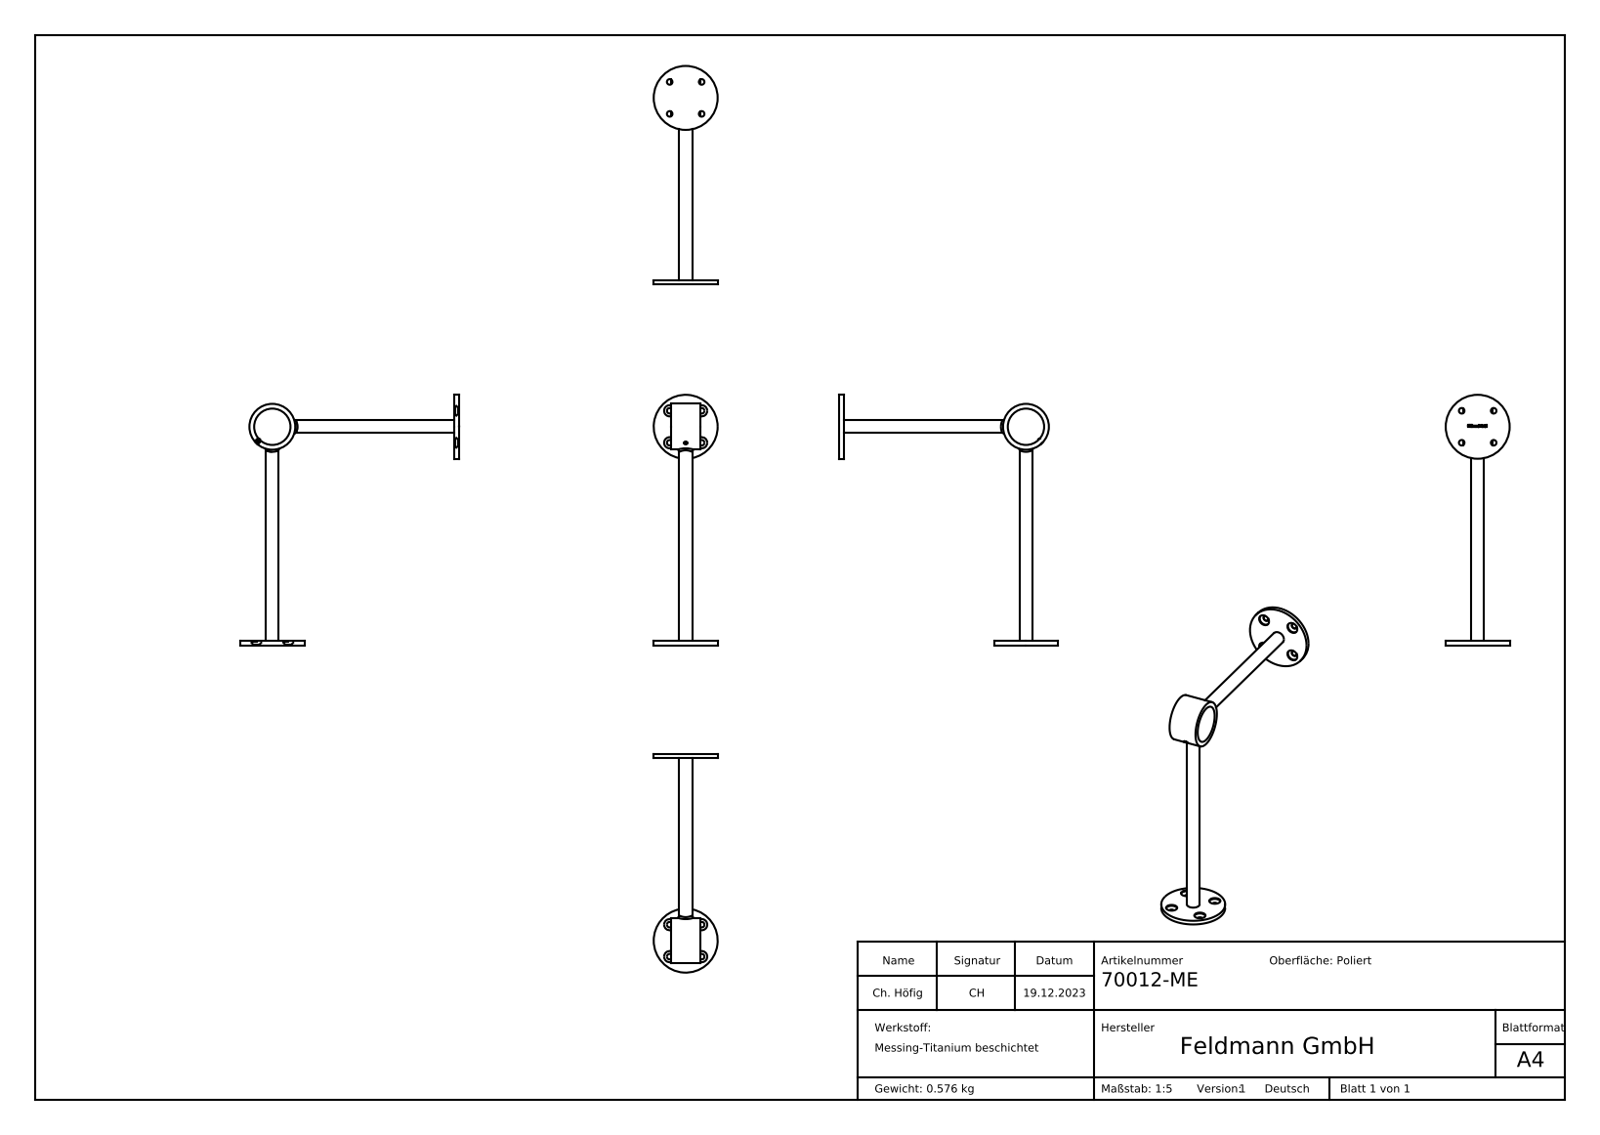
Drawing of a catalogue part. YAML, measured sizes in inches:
part_name: "70012-ME; DIN913_DIN 913 M4x5; 70012-ME Teil1_70012-ME Teil1"
step_written_by: "SolidWorks 2018 (CONFIG_CONTROL_DESIGN)"
units: inches
bodies: {solids: 2, faces: 251, planar: 142, cylindrical: 24, other: 85}
overall_size: [9.252, 8.071, 2.362]
volume: 4.451
surface_area: 50.86
round_holes:
  - {diameter: 0.205, count: 8}
  - {diameter: 0.413, count: 8}
  - {diameter: 0.13, count: 1}
  - {diameter: 1.343, count: 1}
round_bosses_or_shafts:
  - {diameter: 2.362, count: 2}
  - {diameter: 0.472, count: 2}
  - {diameter: 1.693, count: 1}
  - {diameter: 0.157, count: 1}
face_to_face_distances: [0.157, 1.083, 0.079, 0.502, 0.581, 0.154, 0.197, 0.098, 8.071, 7.913]
hole_center_spacings: [1.181, 1.67]
